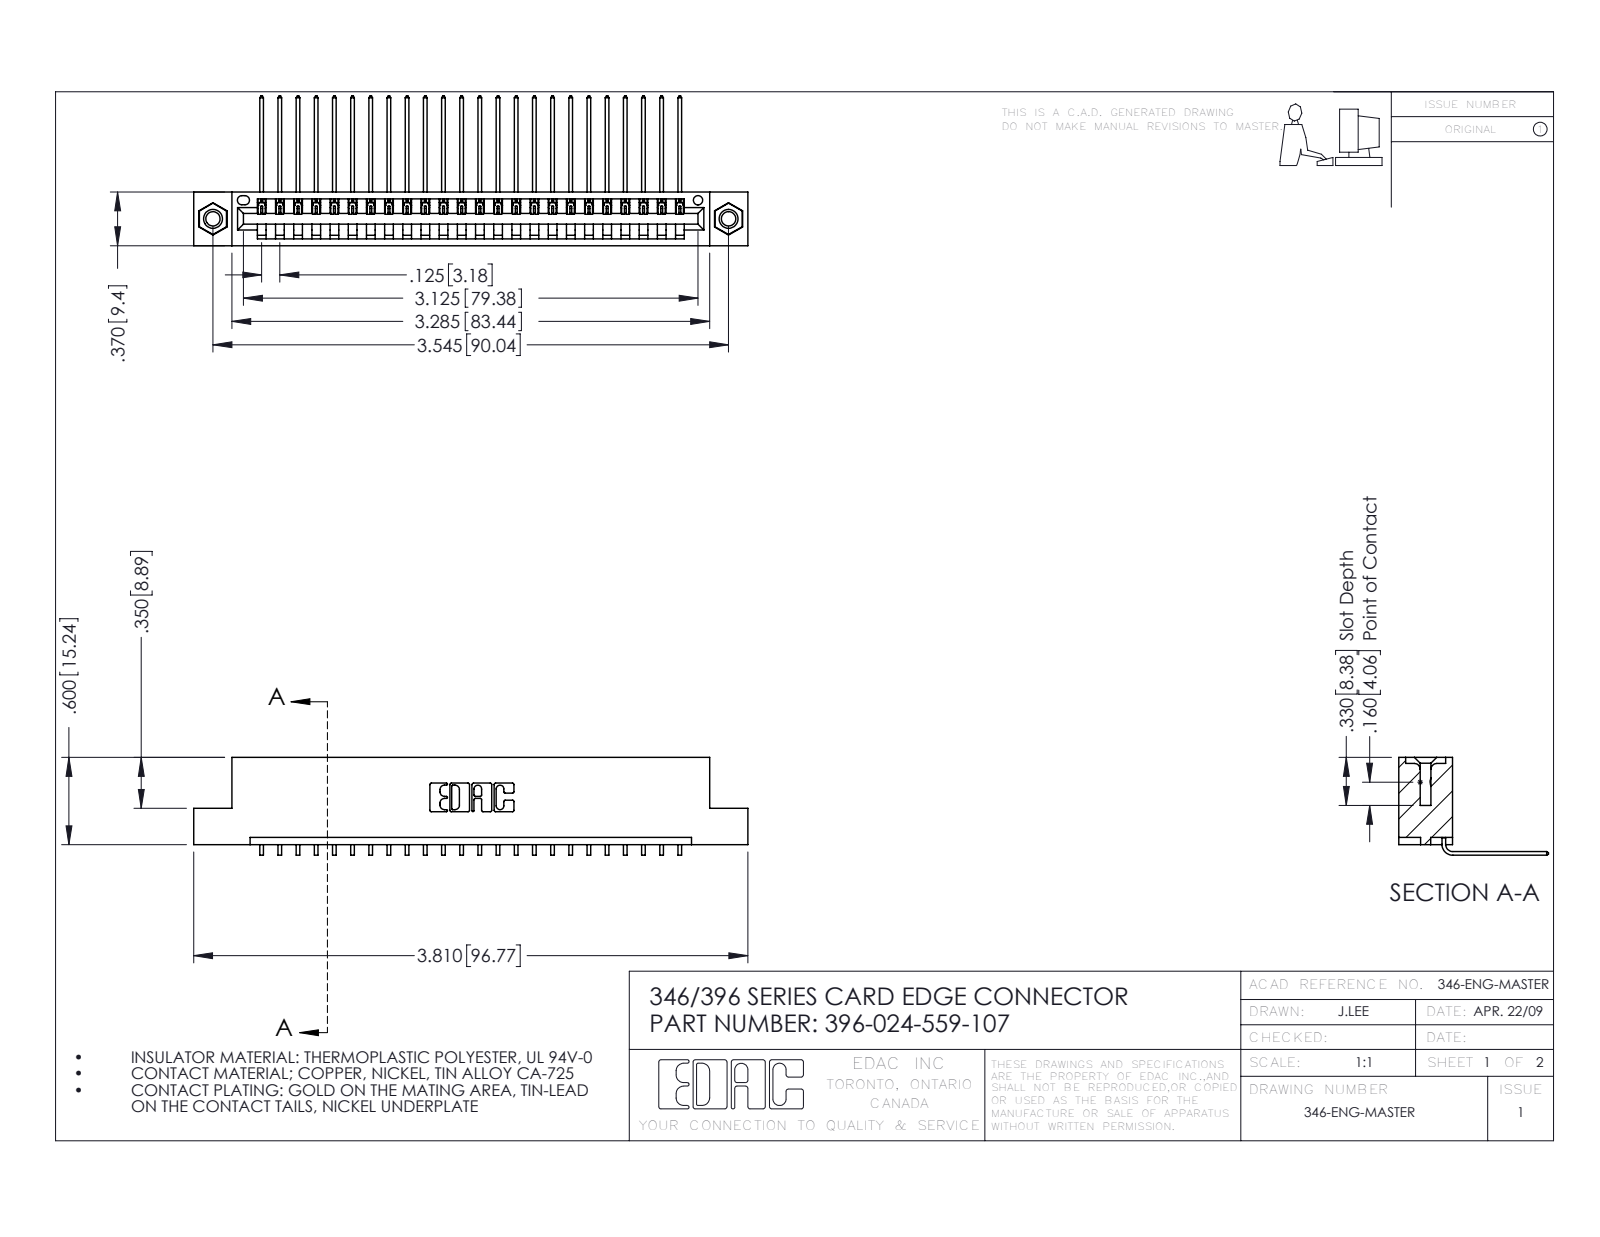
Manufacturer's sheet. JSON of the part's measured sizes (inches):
{"part_name": "346 Part_Flush Mounting Lugs - 0.156 Dia-TI; 396-024-559-107; 345-250-001_345-250-005-103; 345-292-001_558 559 Tail - 1", "step_written_by": "SolidWorks 2016 (CONFIG_CONTROL_DESIGN)", "units": "inches", "bodies": {"solids": 27, "faces": 1622, "planar": 1116, "cylindrical": 490, "other": 16}, "overall_size": [3.81, 1.03, 0.673], "volume_in3": 0.562, "surface_area_in2": 18.33, "round_holes": [[0.098, 2], [0.125, 2], [0.156, 2], [0.064, 1]], "round_bosses_or_shafts": [[0.155, 2]], "partial_cylinders_radius": [[0.006, 48], [0.01, 22], [0.007, 6], [0.031, 6], [0.026, 3], [0.031, 2], [0.04, 2], [0.014, 1]], "face_to_face_distances": [0.048, 0.322, 0.37, 0.25, 0.072, 0.025, 0.298, 0.148, 0.222, 0.1], "hole_center_spacings": [0.246, 3.337, 3.545]}
